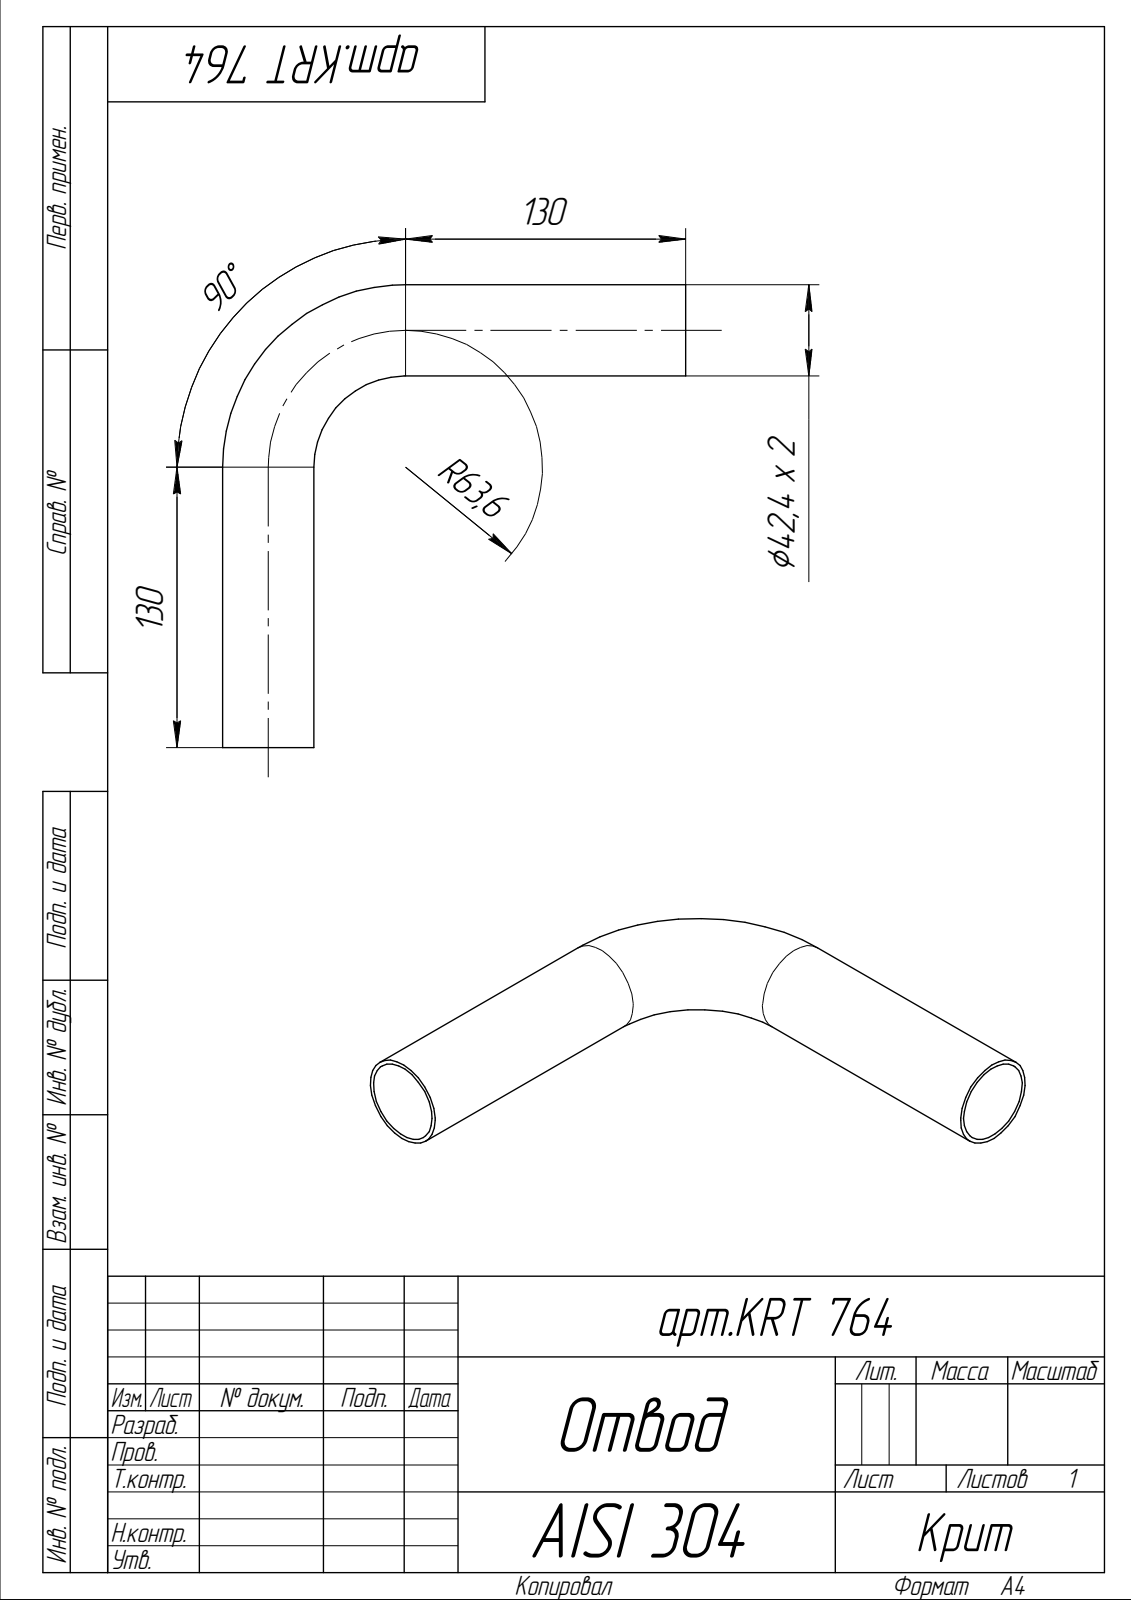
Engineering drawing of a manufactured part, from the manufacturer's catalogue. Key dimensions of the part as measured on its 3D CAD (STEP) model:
Part name (STEP PRODUCT): Деталь
STEP written by: ASCON Math Kernel (AUTOMOTIVE_DESIGN)
Units: millimetres
Bodies: 1 solid, 8 faces (2 planar, 4 cylindrical, 2 other)
Overall size (bounding box): 214.8 × 214.8 × 42.4
Volume: 91 358 mm³ · Surface area: 91 866 mm²
Round holes (diameter × count): ⌀38.4 ×2
Round bosses / shafts (diameter × count): ⌀42.4 ×2
